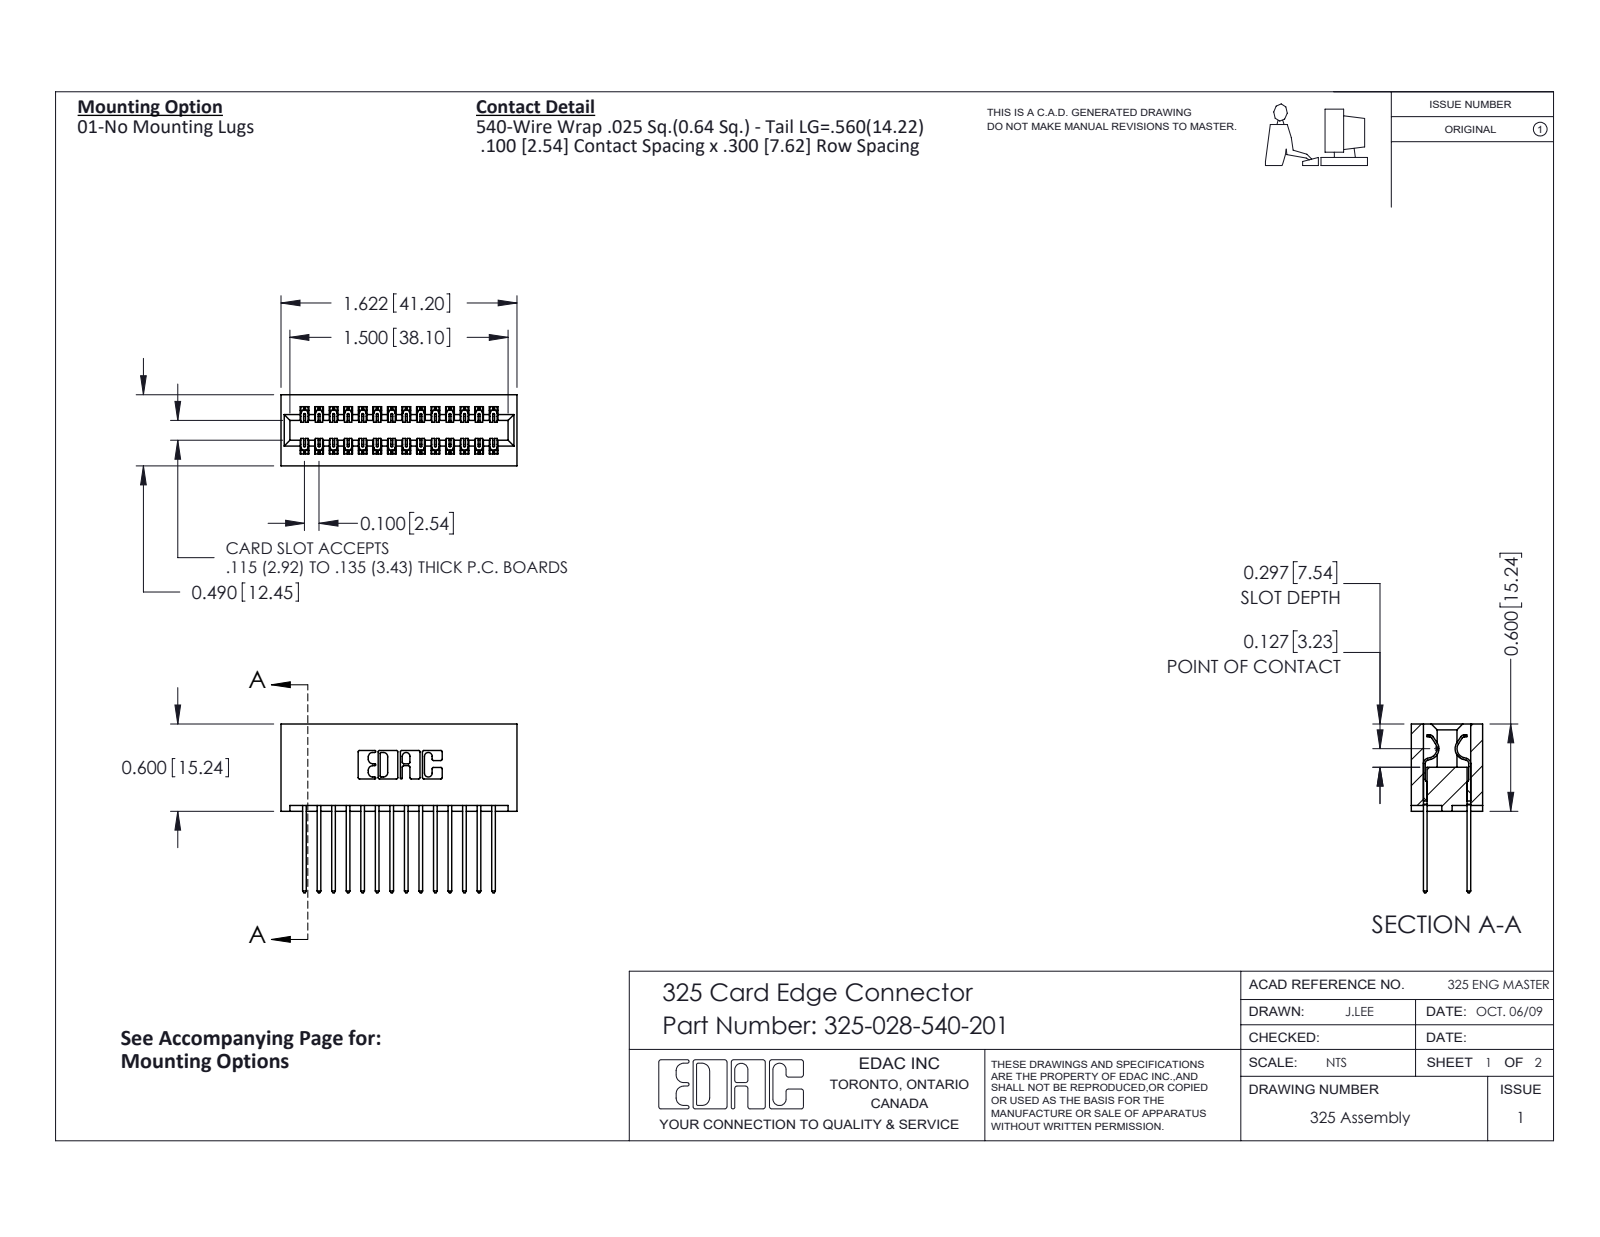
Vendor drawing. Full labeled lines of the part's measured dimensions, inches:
Part name (STEP PRODUCT): 325-292-001_325-293-140; 325-028-540-201; 325 Part_Lugless
STEP written by: SolidWorks 2016 (CONFIG_CONTROL_DESIGN)
Units: inches
Bodies: 29 solids, 1562 faces (1074 planar, 488 cylindrical, 0 other)
Overall size (bounding box): 1.622 × 1.16 × 0.49
Volume: 0.353 in³ · Surface area: 11.62 in²
Partial cylindrical surfaces — rounded edges, fillets, slot ends (radius × count): R0.006 ×42, R0.01 ×28, R0.01 ×22, R0.007 ×6, R0.031 ×6, R0.026 ×3, R0.014 ×2, R0.022 ×2
Main face-to-face distances: 0.083, 0.407, 0.3, 0.107, 0.383, 0.025, 0.325, 0.49, 0.1, 0.2
